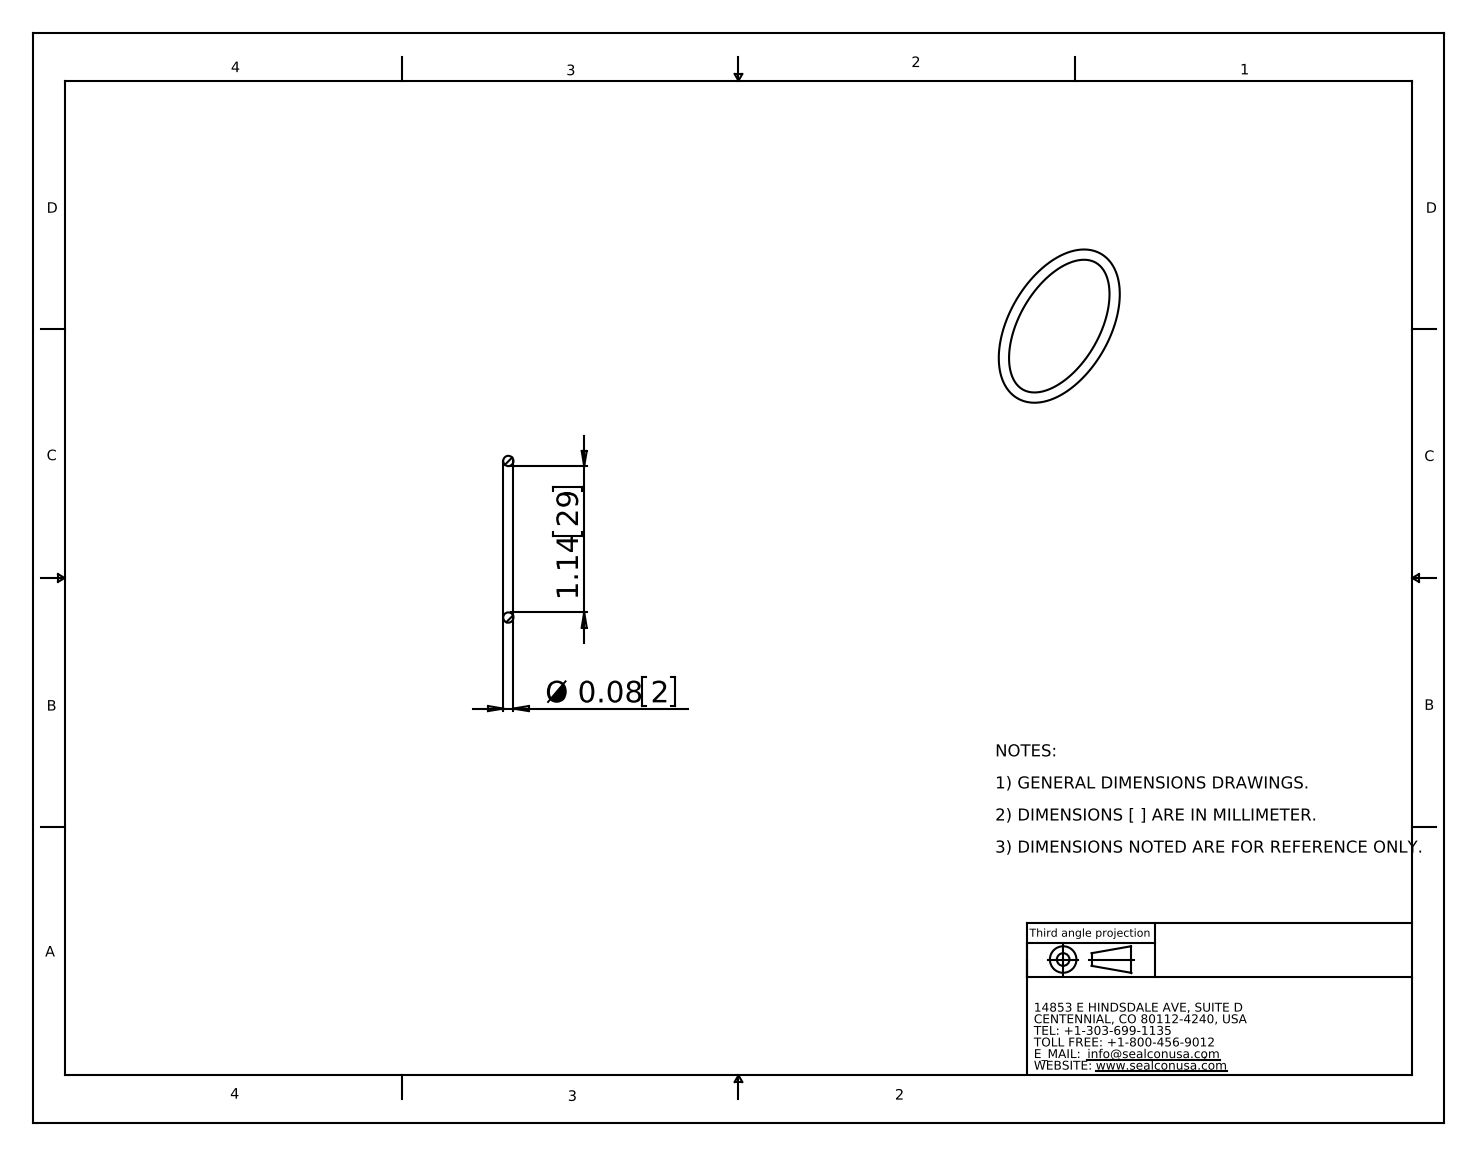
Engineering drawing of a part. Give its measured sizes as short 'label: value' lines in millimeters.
name: OR-10-SI
written by: SolidWorks 2008 (CONFIG_CONTROL_DESIGN)
unit: mm
bodies: 1 solid, 4 faces (0 planar, 0 cylindrical, 4 other)
size: 33 × 33 × 2
volume: 310 mm³; area: 621 mm²
